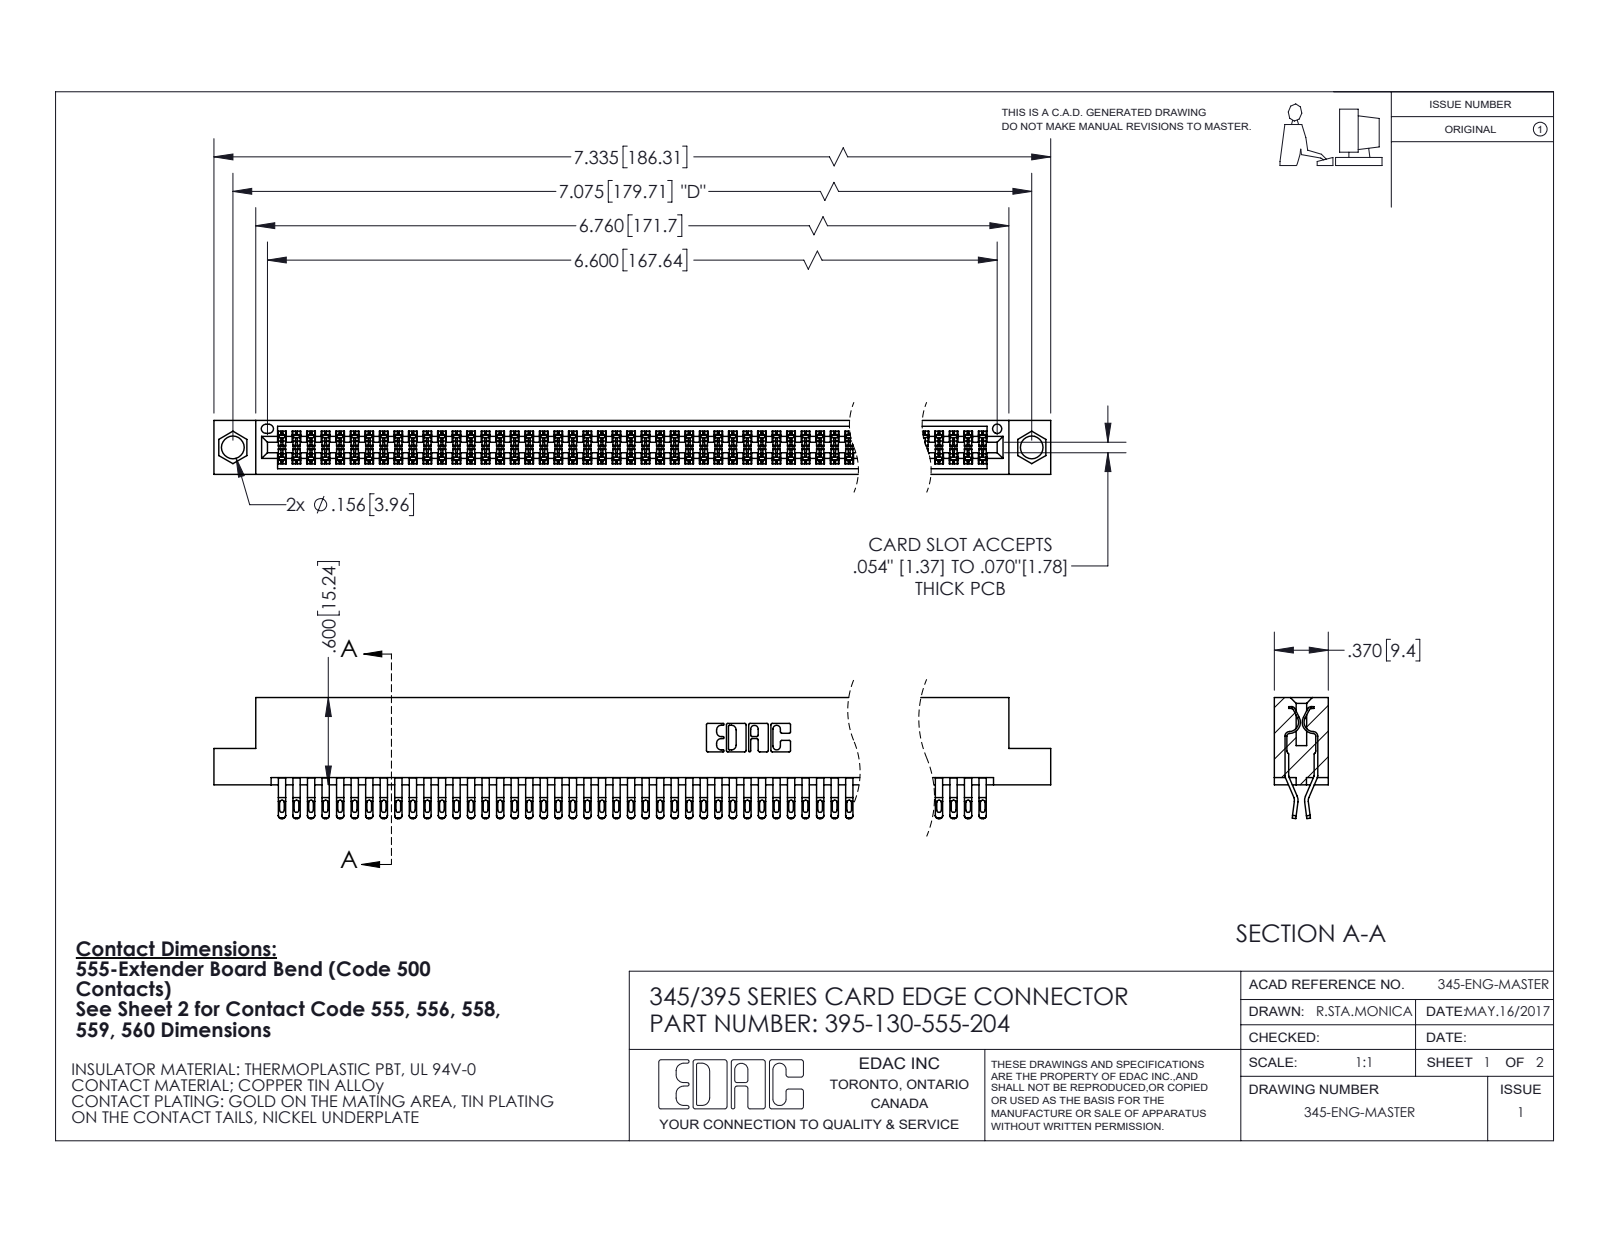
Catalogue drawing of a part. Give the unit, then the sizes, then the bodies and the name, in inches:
Units: inches
Overall size (bounding box): 7.335 × 0.832 × 0.37
Round holes (diameter × count): ⌀0.156 ×2, ⌀0.064 ×1
Partial cylindrical surfaces — rounded edges, fillets, slot ends (radius × count): R0.016 ×325, R0.006 ×260, R0.02 ×260, R0.01 ×22, R0.007 ×6, R0.031 ×6, R0.026 ×3, R0.01 ×2
Main face-to-face distances: 0.298, 0.072, 0.025, 0.37, 0.2, 0.098, 0.272, 0.225, 0.175, 0.149
Hole centre spacings: 0.27, 6.839, 7.075
Volume: 1.134 in³ · Surface area: 45.07 in²
Bodies: 131 solids, 7420 faces (4124 planar, 3296 cylindrical, 0 other)
Part name (STEP PRODUCT): 345 Part_Flush Mounting Lugs - 0.156 Dia-TI; 395-130-555-204; 345-292-001_555 Tail
STEP written by: SolidWorks 2020 (CONFIG_CONTROL_DESIGN)
